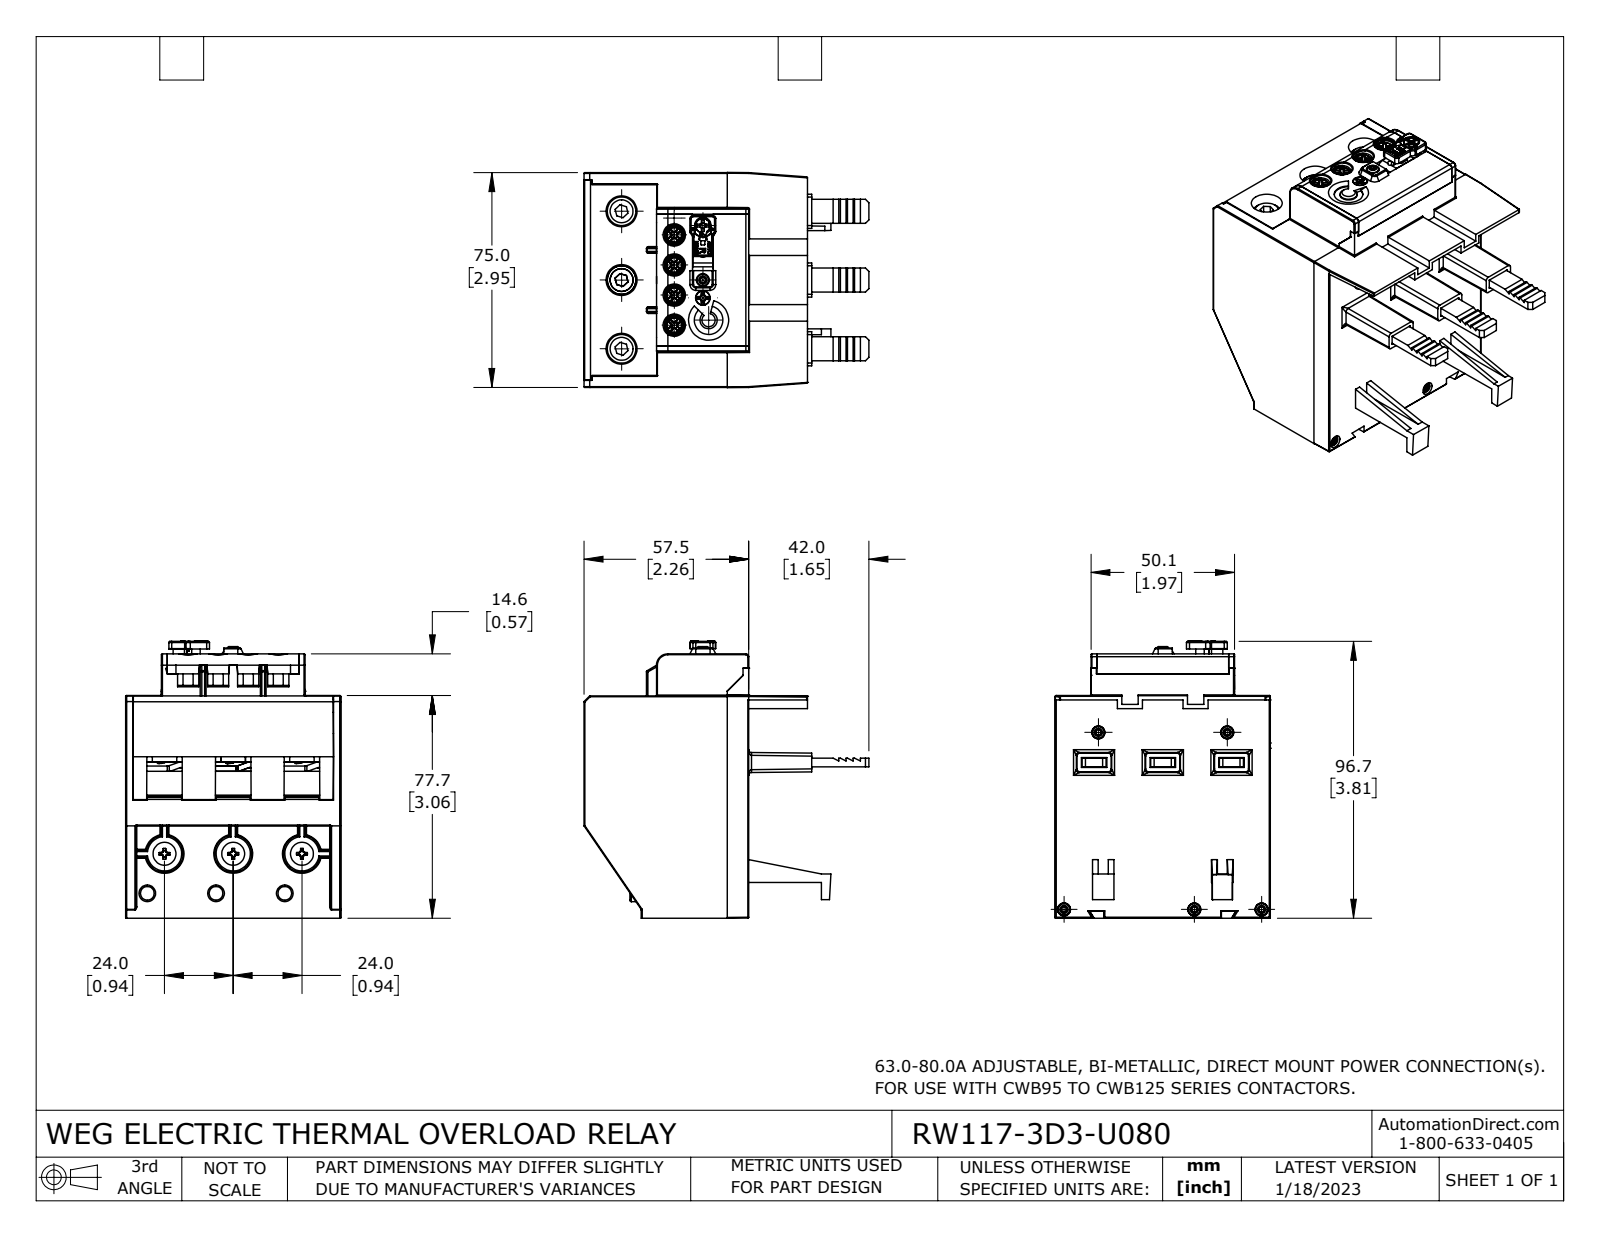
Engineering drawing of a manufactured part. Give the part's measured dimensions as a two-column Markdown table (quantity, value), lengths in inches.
| quantity | value |
| --- | --- |
| part name | RW117-3D3-U080 |
| STEP written by | SolidWorks 2021 (CONFIG_CONTROL_DESIGN) |
| units | inches |
| bodies | 48 solids, 2642 faces (1423 planar, 718 cylindrical, 501 other) |
| overall size | 3.925 × 3.815 × 2.958 |
| volume | 17.93 in³ |
| surface area | 158.2 in² |
| round holes (diameter × count) | 0.091 × 5, 0.071 × 4, 0.126 × 4, 0.169 × 3, 0.315 × 3, 0.356 × 3, 0.425 × 3, 0.098 × 2, 0.173 × 1, 0.177 × 1, 0.199 × 1, 0.201 × 1 |
| round bosses / shafts (diameter × count) | 0.157 × 6, 0.083 × 6, 0.169 × 4, 0.138 × 4, 0.107 × 4, 0.512 × 3, 0.504 × 3, 0.394 × 3 |
| partial cylindrical surfaces (radius × count) | 0.012 × 123, 0.02 × 59, 0.013 × 36, 0.004 × 32, 0.039 × 32, 0.008 × 22, 0.094 × 12, 0.016 × 11 |
| main face-to-face distances | 0.295, 0.945, 2.953, 0.075, 0.657, 0.583, 0.933, 1.89, 0.287, 0.059 |
| hole center spacings | 0.945, 0.413, 0.593, 0.893, 1.89, 0.444, 0.735, 0.753 |
